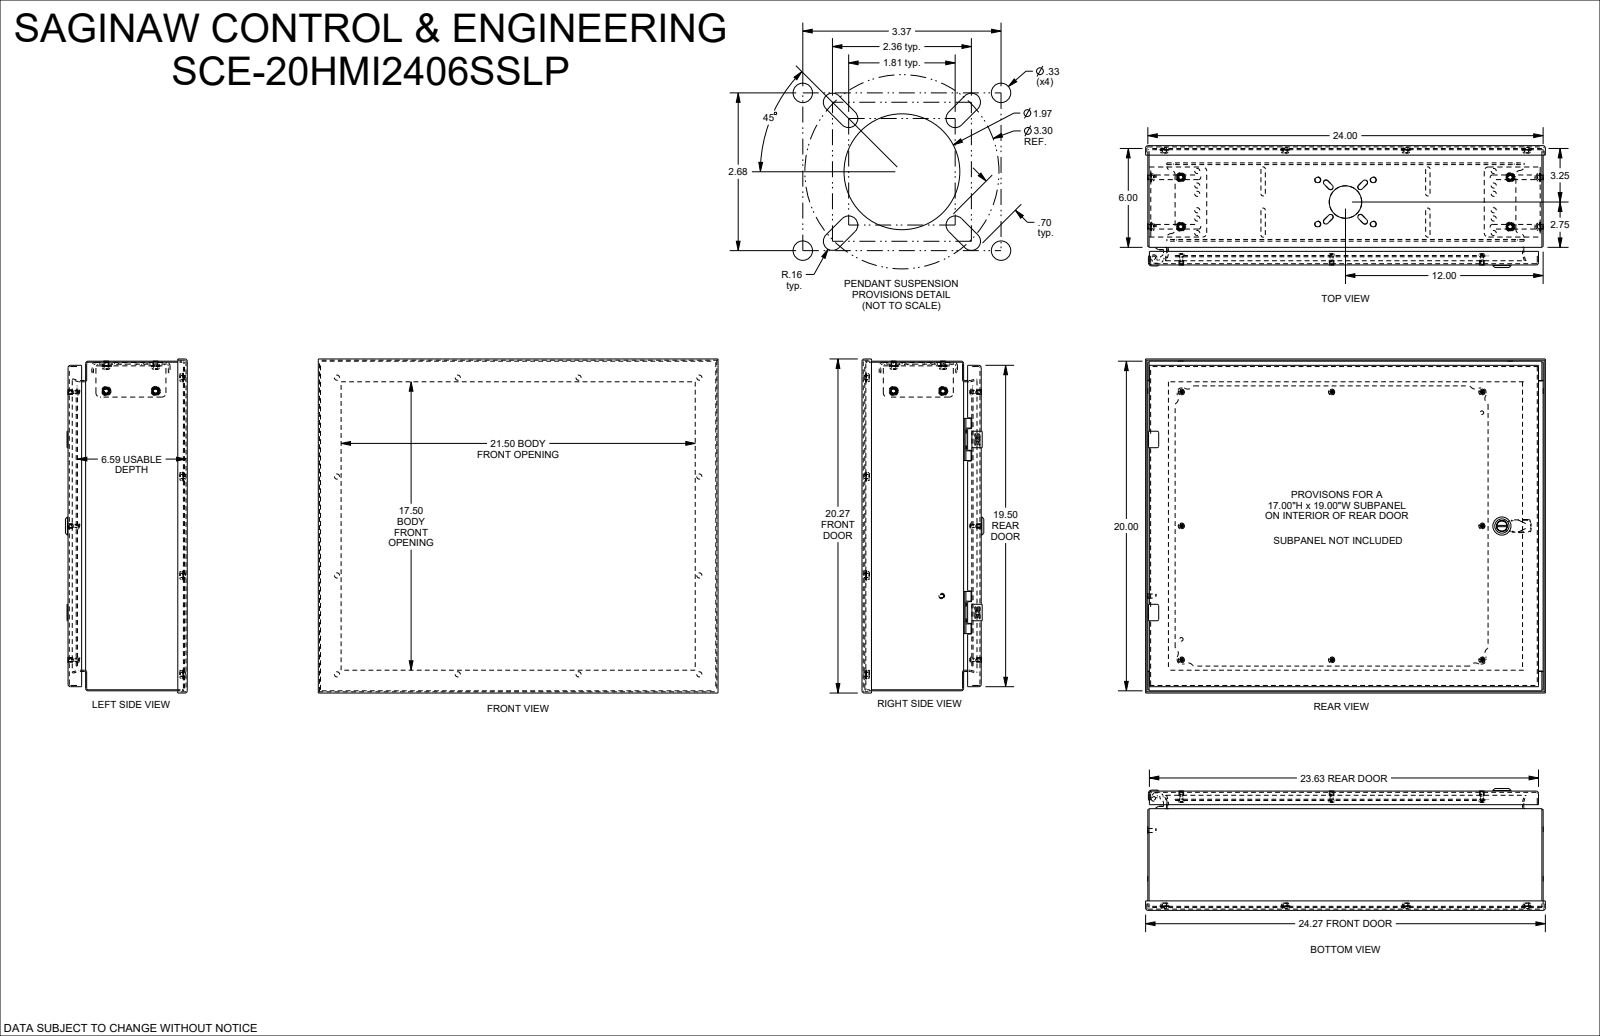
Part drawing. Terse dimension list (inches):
name: SCE-20HMI2406LP
written by: SolidWorks 2023 (AUTOMOTIVE_DESIGN)
unit: in
bodies: 24 solids, 2269 faces (1110 planar, 714 cylindrical, 445 other)
size: 24.27 × 20.27 × 7.395
volume: 187.4 in³; area: 4 692 in²
holes: 12× ⌀0.31, 12× ⌀0.313, 8× ⌀0.19, 8× ⌀0.25, 7× ⌀0.25, 4× ⌀0.172, 4× ⌀0.205, 4× ⌀0.218, 4× ⌀0.244, 4× ⌀0.266, 4× ⌀0.27, 4× ⌀0.281
bosses: 19× ⌀0.248, 8× ⌀0.373, 8× ⌀0.28, 8× ⌀0.188, 7× ⌀0.337, 6× ⌀0.17, 4× ⌀0.25, 4× ⌀0.24
rounds: 30× R0.012, 28× R0.25, 24× R0.015, 16× R0.22, 13× R0.06, 12× R0.02, 12× R0.1, 12× R0.141
face distances: 0.075, 6.667, 0.06, 7.163, 7.103, 7.178, 7.238, 0.496, 0.436, 6.742
hole spacings: 18, 6, 22.804, 0.494, 0.5, 0.883, 1.071, 1.118
